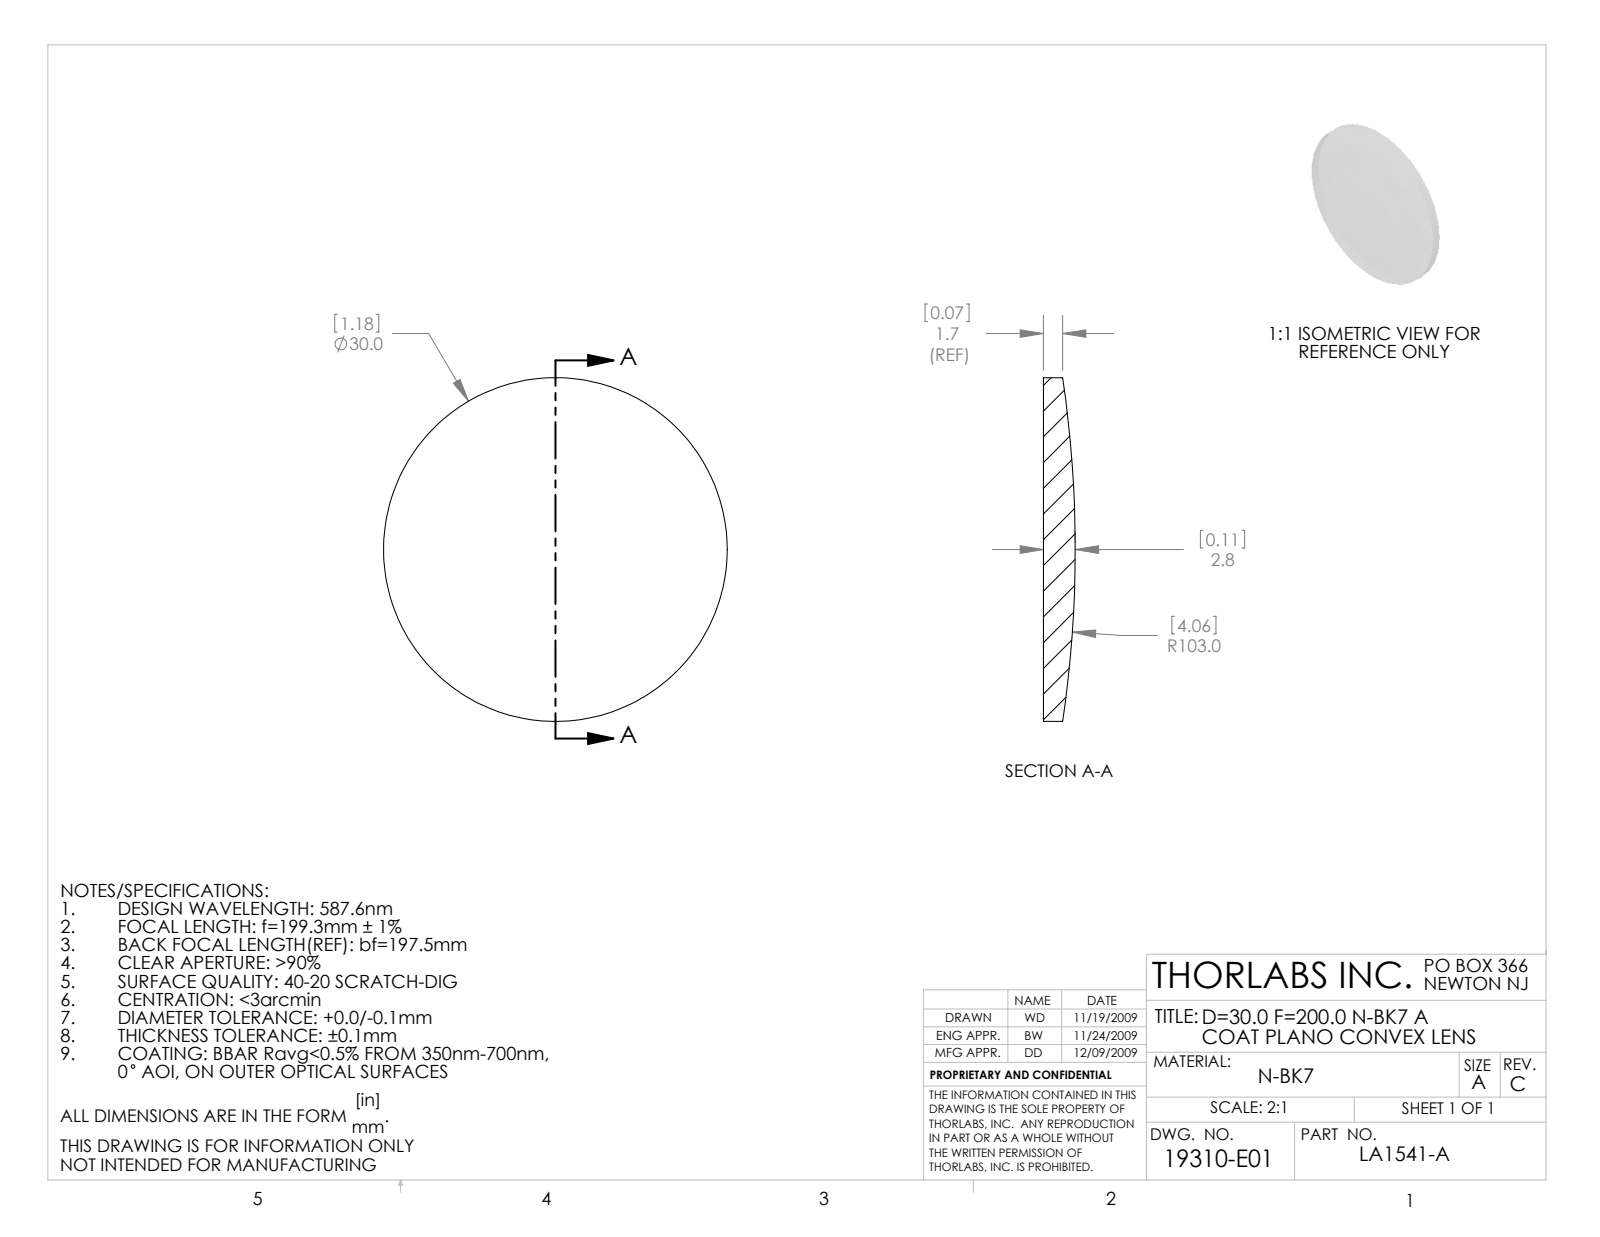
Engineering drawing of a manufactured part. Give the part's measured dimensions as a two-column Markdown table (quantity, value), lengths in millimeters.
| quantity | value |
| --- | --- |
| part name | 19310-E0W |
| STEP written by | SolidWorks 2009 (AUTOMOTIVE_DESIGN) |
| units | millimeters |
| bodies | 1 solid, 5 faces (1 planar, 2 cylindrical, 2 other) |
| overall size | 30 × 30 × 2.78 |
| volume | 1 578 mm³ |
| surface area | 1 576 mm² |
| round bosses / shafts (diameter × count) | 30 × 1 |
